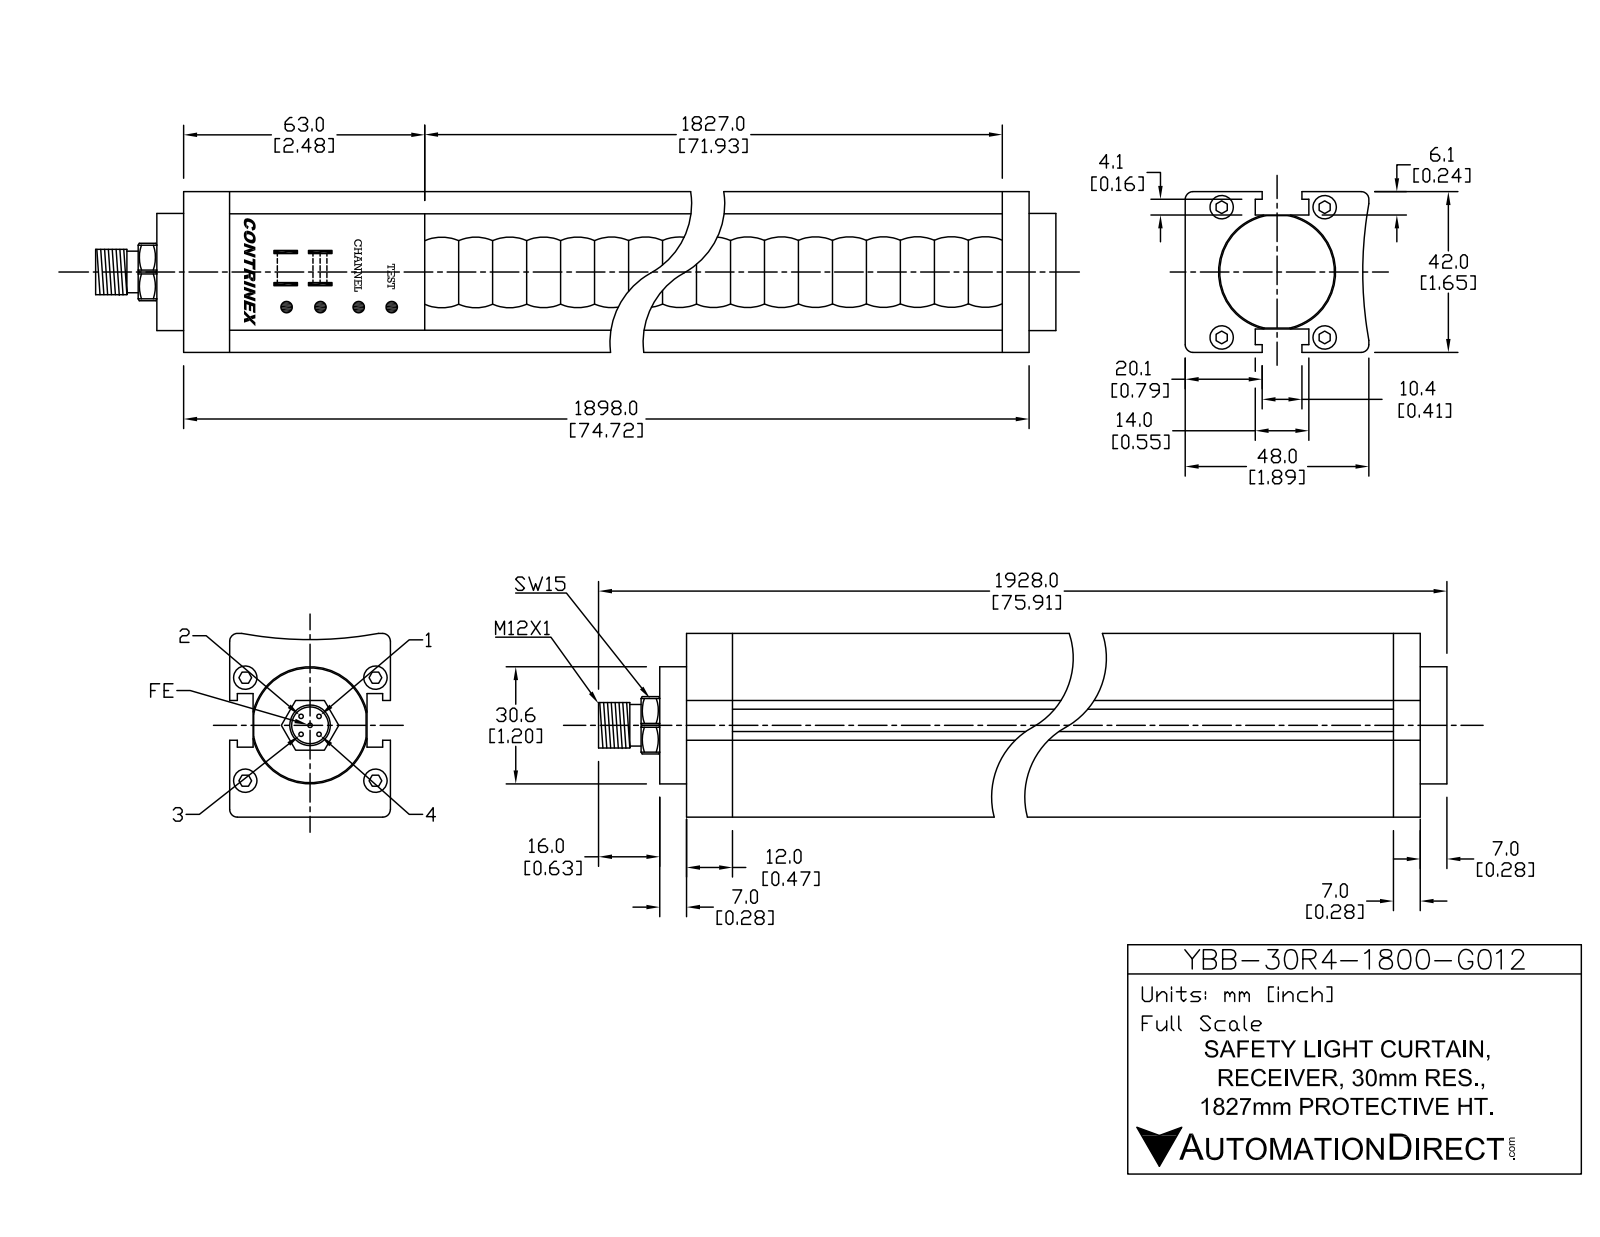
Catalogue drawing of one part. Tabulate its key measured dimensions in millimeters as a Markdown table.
| quantity | value |
| --- | --- |
| part name | YBB-30R4-1800-G012 |
| STEP written by | SolidWorks 2016 (AUTOMOTIVE_DESIGN) |
| units | millimeters |
| bodies | 19 solids, 440 faces (208 planar, 168 cylindrical, 64 other) |
| overall size | 1928 × 48 × 42 |
| volume | 3 408 000 mm³ |
| surface area | 422 228 mm² |
| round holes (diameter × count) | 6 × 4, 8.5 × 1, 32 × 1 |
| round bosses / shafts (diameter × count) | 1 × 5, 5.5 × 4, 30.6 × 1, 12 × 1, 10.5 × 1 |
| partial cylindrical surfaces (radius × count) | 1 × 48, 0.5 × 4, 0.55 × 2, 8.2 × 1, 100 × 1 |
| main face-to-face distances | 6.3, 35.7, 42, 29.4, 14, 17.2, 31.2, 15.7, 29.7, 46.9 |
| hole center spacings | 21.04, 22.34, 26.9, 34, 43.35 |
